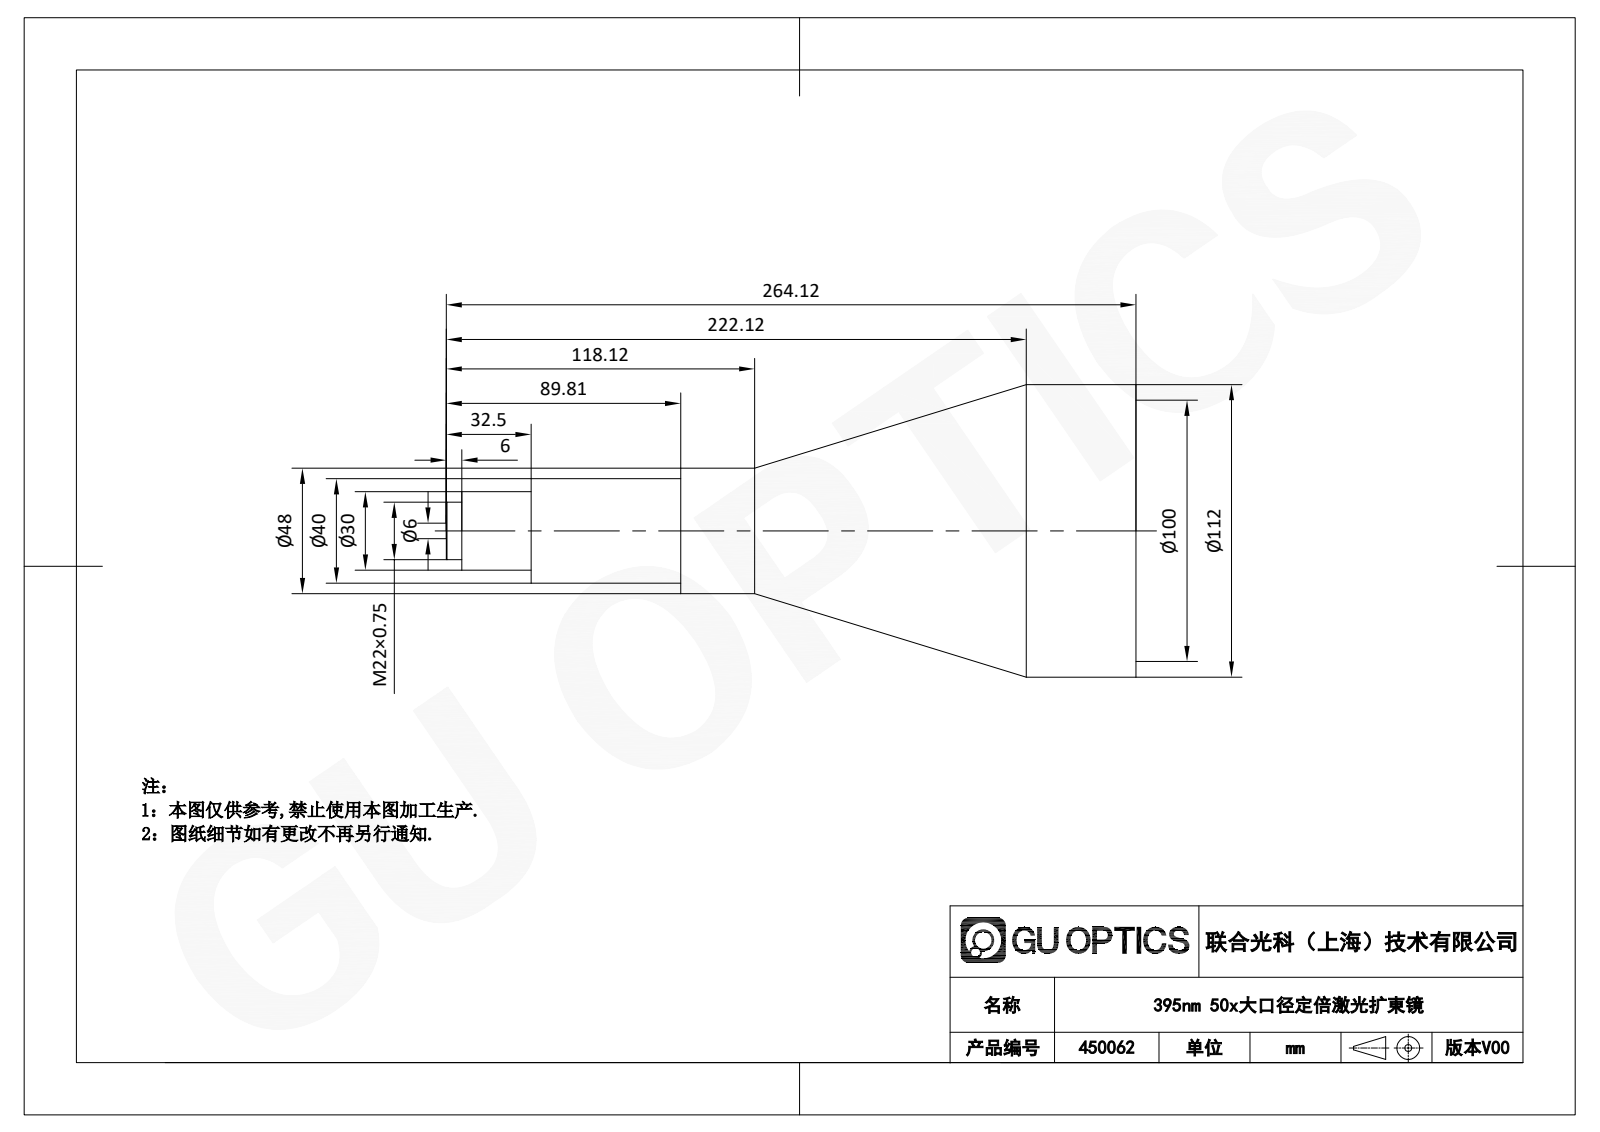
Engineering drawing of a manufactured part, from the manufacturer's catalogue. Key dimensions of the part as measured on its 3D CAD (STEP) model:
Part name (STEP PRODUCT): 450062
STEP written by: SolidWorks 2020 (AUTOMOTIVE_DESIGN)
Units: millimetres
Bodies: 1 solid, 23 faces (7 planar, 14 cylindrical, 2 other)
Overall size (bounding box): 264.12 × 112 × 112
Volume: 1 101 000 mm³ · Surface area: 68 503 mm²
Round holes (diameter × count): ⌀6 ×1, ⌀100 ×1
Round bosses / shafts (diameter × count): ⌀112 ×1, ⌀48 ×1, ⌀40 ×1, ⌀30 ×1, ⌀22 ×1
Main face-to-face distances: 1, 173.31, 174.31, 57.31, 230.62, 231.62, 263.12, 32.5, 89.81, 264.12
